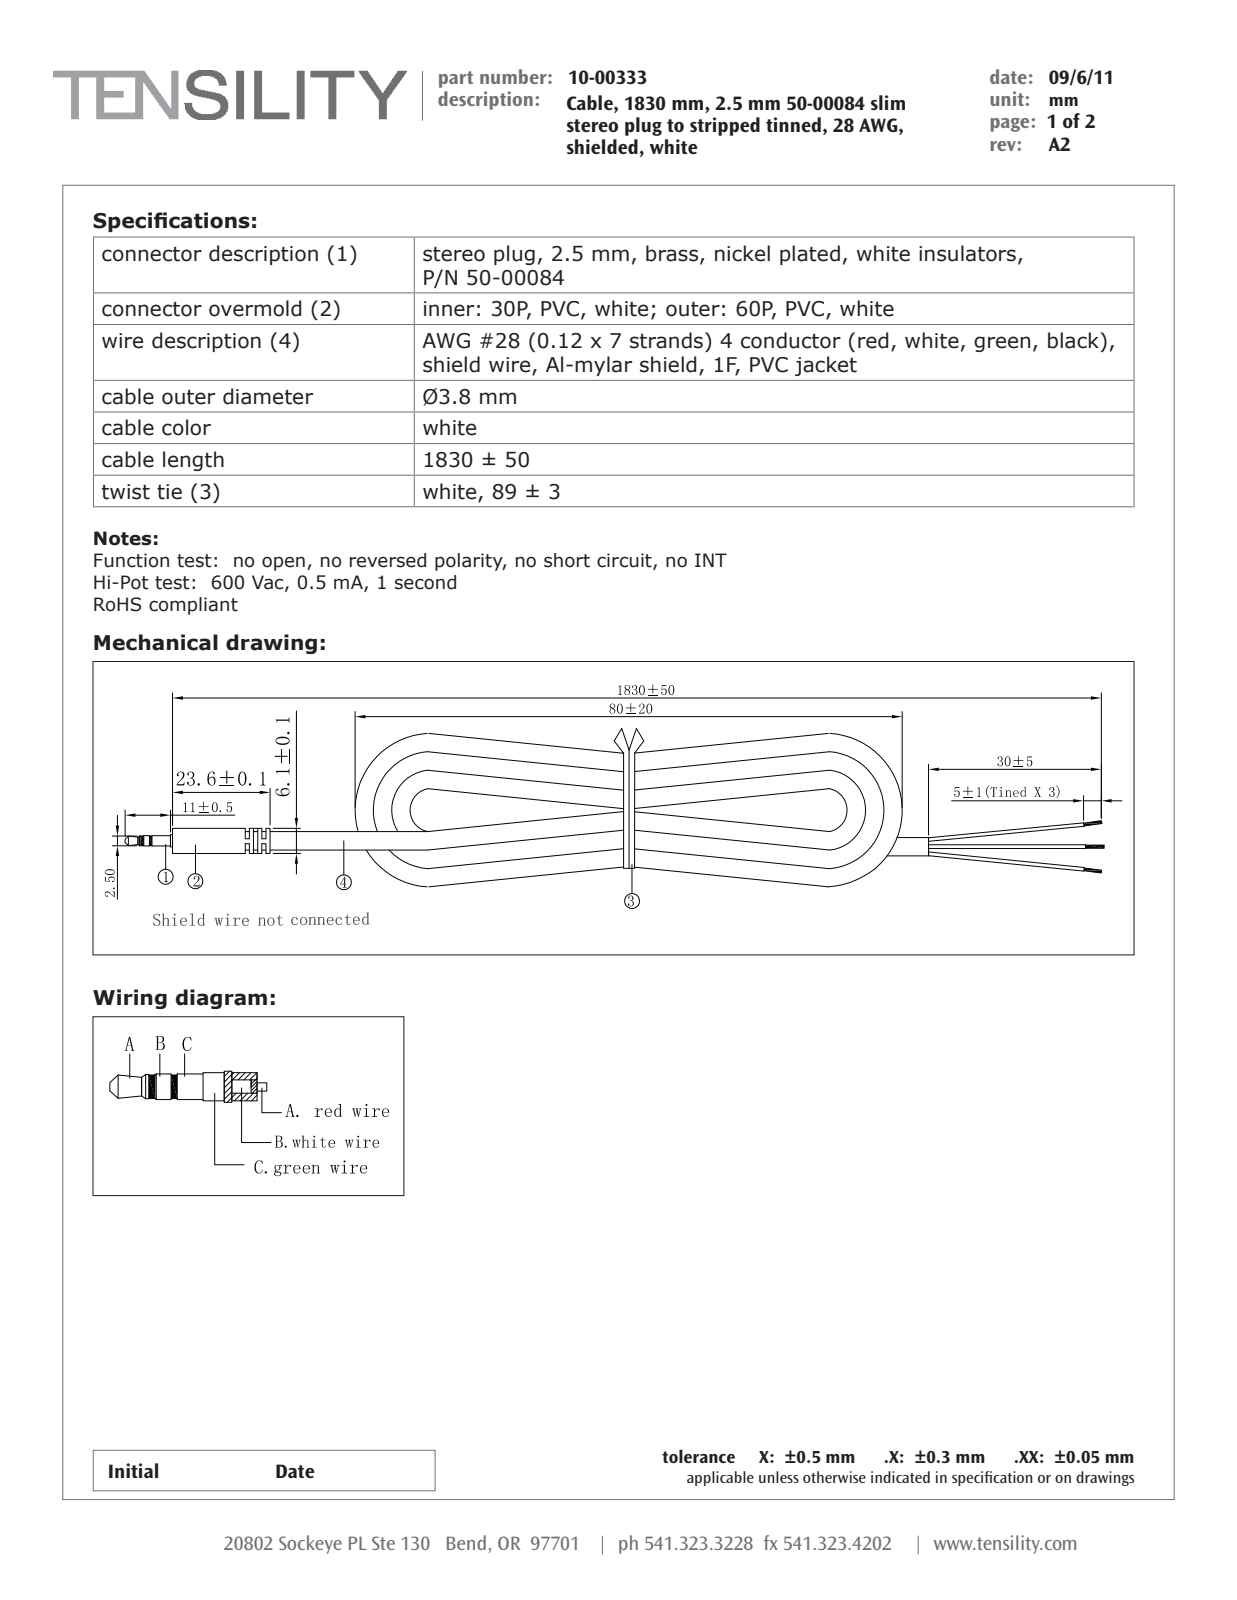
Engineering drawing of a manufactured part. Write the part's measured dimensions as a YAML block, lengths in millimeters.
part_name: "24-00028; 50-00406; 10-00333_revA5; 30-00180_no heat shrink, no shield"
step_written_by: "SolidWorks 2015 (CONFIG_CONTROL_DESIGN)"
units: millimeters
bodies: {solids: 98, faces: 691, planar: 258, cylindrical: 379, other: 54}
overall_size: [209.4, 6.1, 6.1]
volume: 2448
surface_area: 16425
round_holes:
  - {diameter: 0.85, count: 3}
  - {diameter: 1.2, count: 1}
  - {diameter: 1.86, count: 1}
  - {diameter: 1.91, count: 1}
round_bosses_or_shafts:
  - {diameter: 6.1, count: 1}
  - {diameter: 5.8, count: 1}
  - {diameter: 4.5, count: 1}
  - {diameter: 3.8, count: 1}
  - {diameter: 3.57, count: 1}
  - {diameter: 3, count: 1}
  - {diameter: 2.99, count: 1}
  - {diameter: 2.5, count: 1}
partial_cylinders:
  - {radius: 0.1, count: 4}
  - {radius: 0.85, count: 1}
  - {radius: 1, count: 1}
  - {radius: 2, count: 1}
face_to_face_distances: [0.9, 1.8, 2.7, 3.6, 4.5, 17.9, 18.8, 19.7, 5.4, 23.3]
hole_center_spacings: [1.03, 0.96, 0.43, 0.7, 1.09, 0.57, 1.32, 0.83]
